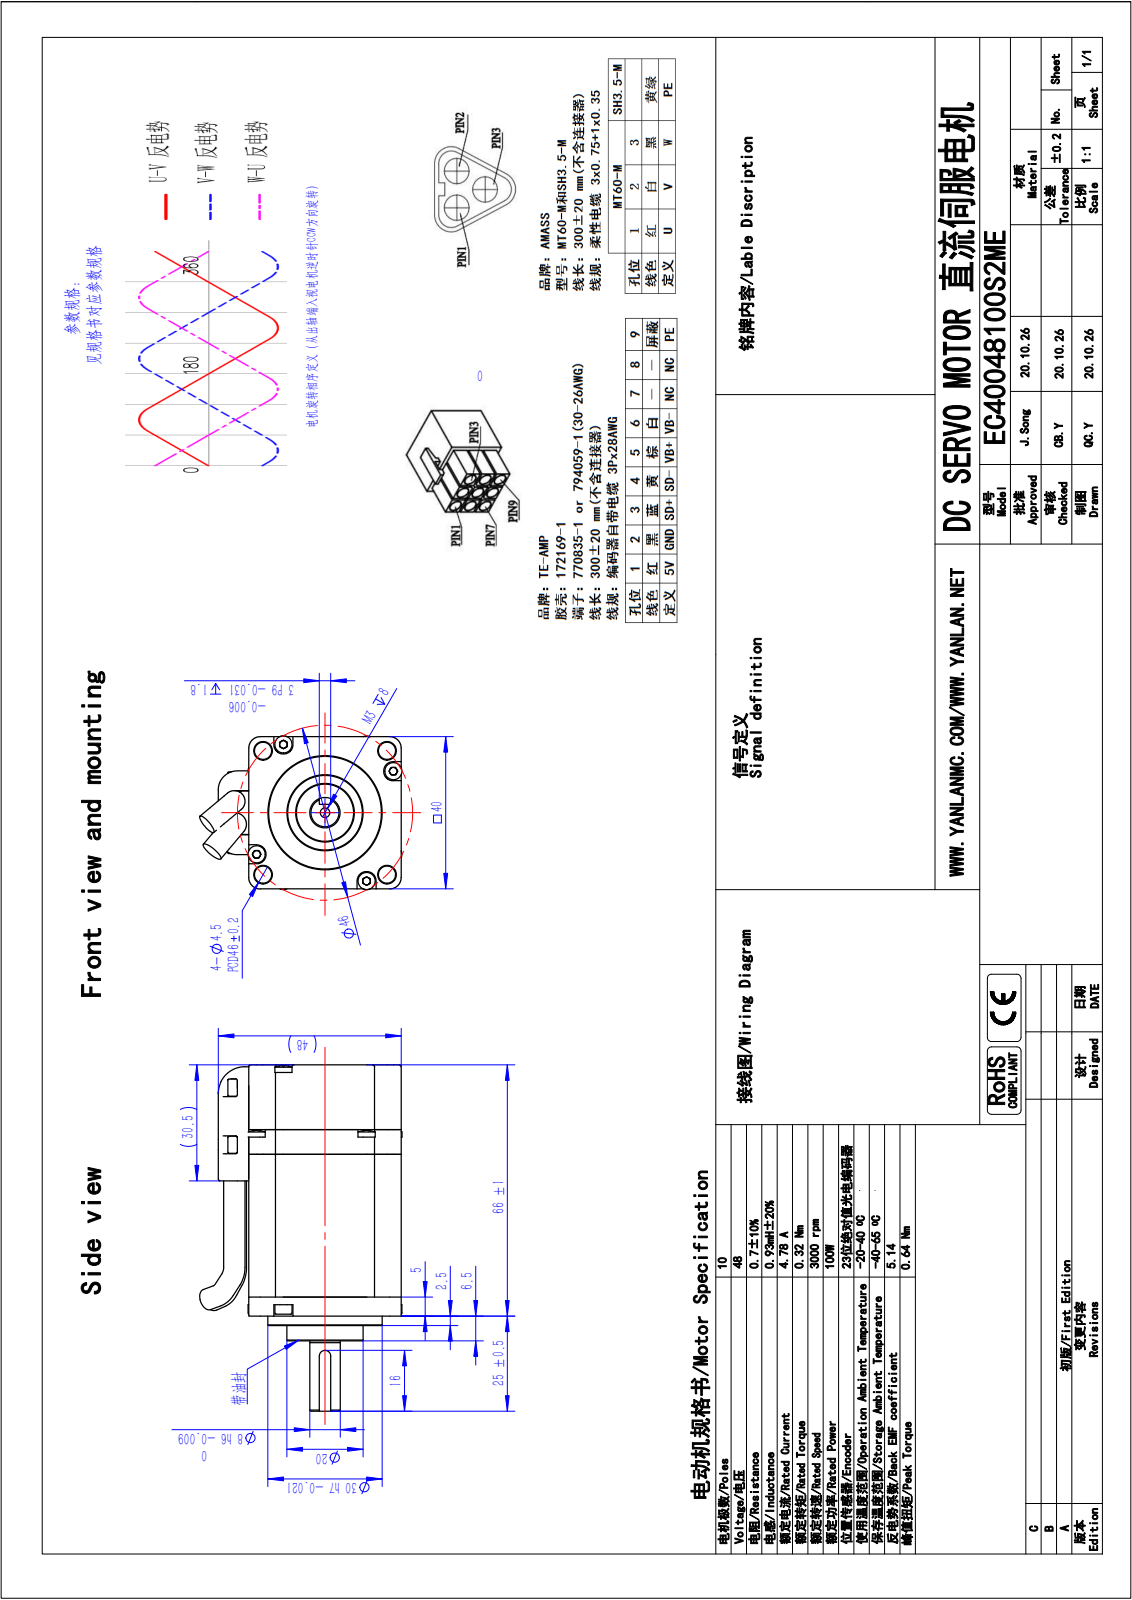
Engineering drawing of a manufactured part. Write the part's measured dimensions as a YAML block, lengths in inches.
part_name: "M3X12_M3X12; M3X10_M3X10; 40直流伺服电机-100W-48V-17位多圈绝对值-YET-PDF; Цб"
step_written_by: "SolidWorks 2020 (AUTOMOTIVE_DESIGN)"
units: inches
bodies: {solids: 13, faces: 478, planar: 265, cylindrical: 157, other: 56}
overall_size: [3.583, 1.96, 1.575]
volume: 6.016
surface_area: 40.45
round_holes:
  - {diameter: 0.098, count: 4}
  - {diameter: 0.134, count: 4}
  - {diameter: 0.177, count: 4}
  - {diameter: 0.236, count: 4}
  - {diameter: 0.63, count: 1}
round_bosses_or_shafts:
  - {diameter: 0.118, count: 8}
  - {diameter: 0.22, count: 4}
  - {diameter: 0.217, count: 4}
  - {diameter: 0.197, count: 4}
  - {diameter: 0.157, count: 2}
  - {diameter: 1.181, count: 1}
  - {diameter: 0.787, count: 1}
  - {diameter: 0.315, count: 1}
partial_cylinders:
  - {radius: 0.012, count: 16}
  - {radius: 0.118, count: 14}
  - {radius: 0.039, count: 8}
  - {radius: 0.059, count: 5}
  - {radius: 0.315, count: 3}
face_to_face_distances: [1.575, 1.417, 0.315, 1.26, 0.787, 2.205, 0.945, 0.394, 2.598, 1.811]
hole_center_spacings: [0.325, 0.63, 0.704, 0.906, 0.955, 1.28, 1.311, 1.589]
